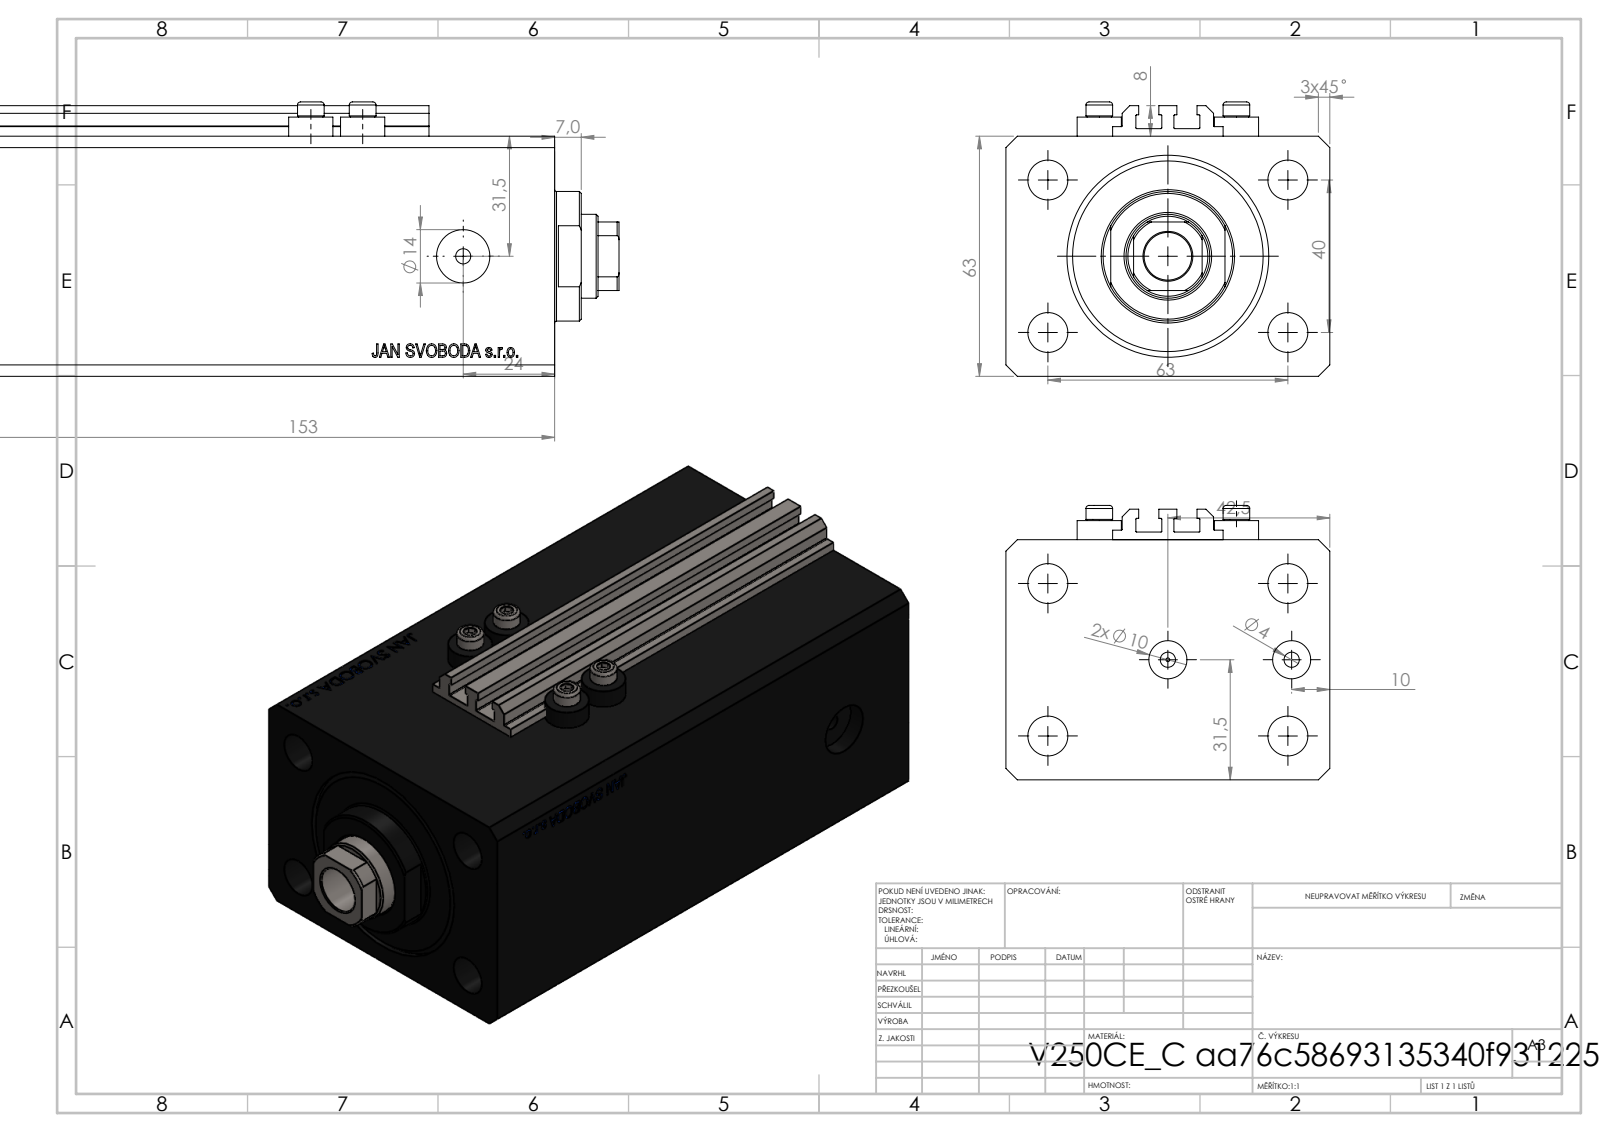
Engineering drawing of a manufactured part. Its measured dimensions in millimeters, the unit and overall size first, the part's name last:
Units: millimetres
Overall size (bounding box): 169.9 × 85 × 72
Round holes (diameter × count): ⌀4 ×8, ⌀10.5 ×4, ⌀10 ×2, ⌀14 ×2, ⌀1.25 ×1, ⌀12.5 ×1, ⌀22 ×1, ⌀40 ×1, ⌀53 ×1
Round bosses / shafts (diameter × count): ⌀11.6 ×4, ⌀7 ×4, ⌀34 ×1
Partial cylindrical surfaces — rounded edges, fillets, slot ends (radius × count): R0.2 ×10, R10.5 ×1
Main face-to-face distances: 63, 85, 153, 125.9, 27.1, 11.4, 114.5, 141.6, 2.5, 2
Hole centre spacings: 37.31, 13.6, 20.02, 36, 38.48, 40, 63, 67.05
Volume: 714 111 mm³ · Surface area: 137 811 mm²
Bodies: 8 solids, 1038 faces (504 planar, 88 cylindrical, 446 other)
Part name (STEP PRODUCT): V250CE_C_Body; V250CE_VC_C; ALLEN BOLT V250CE; V250CE_C_VCP
STEP written by: SolidWorks 2019 (CONFIG_CONTROL_DESIGN)
